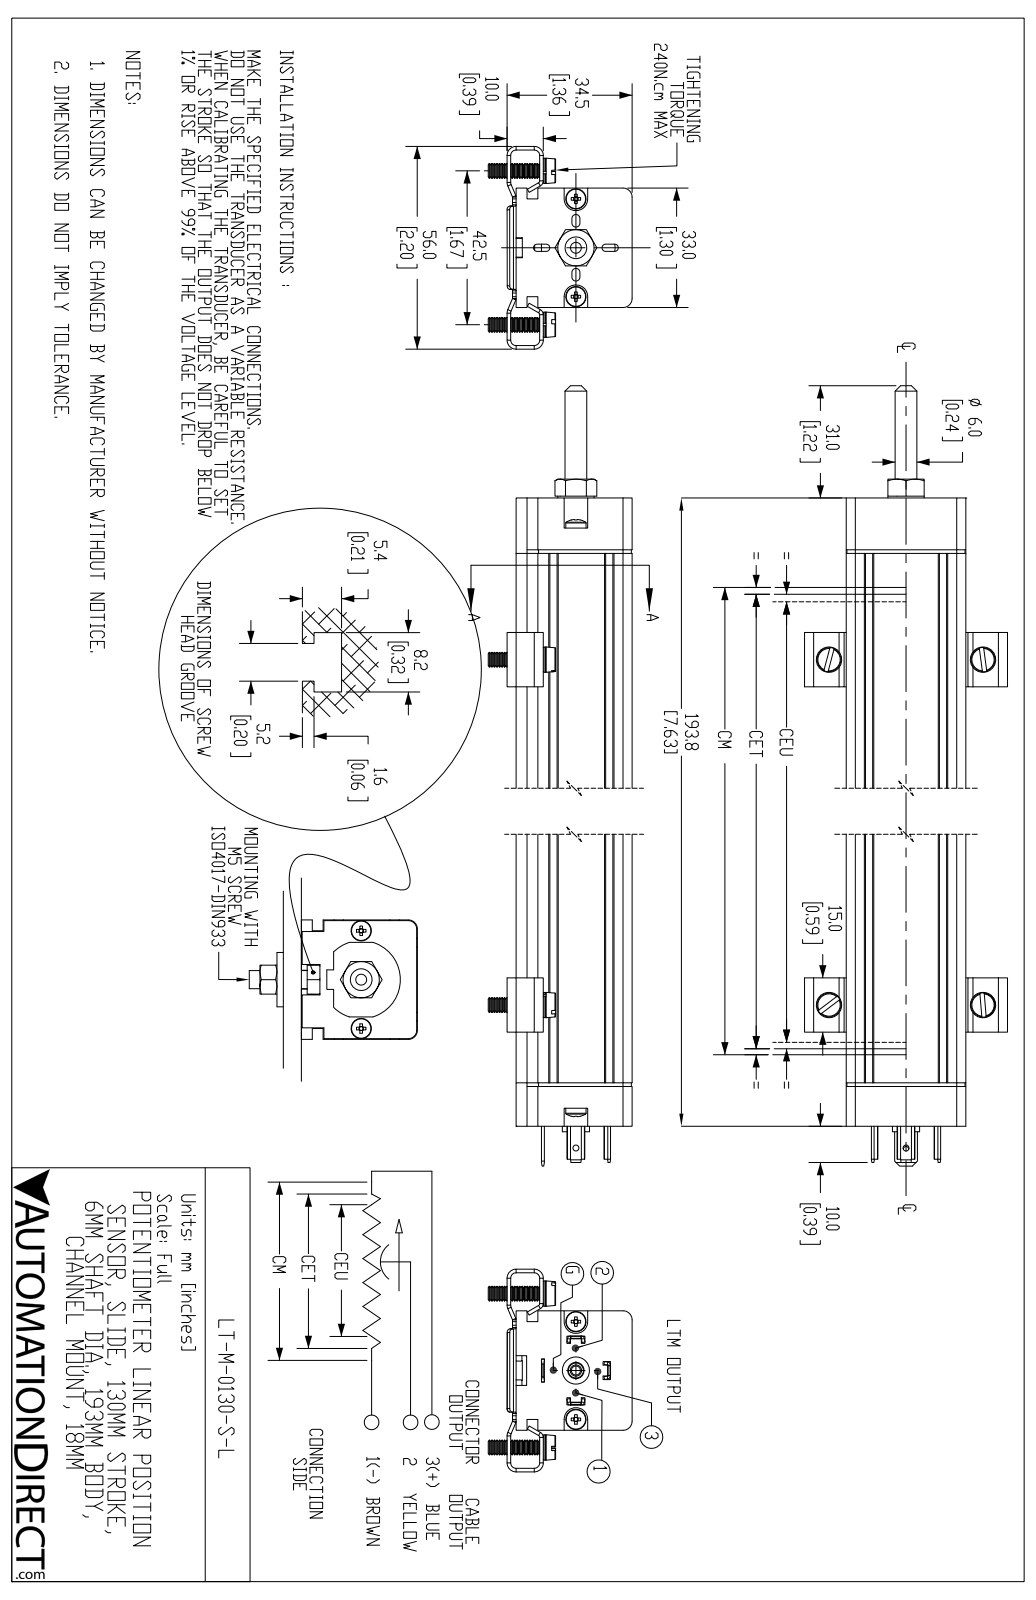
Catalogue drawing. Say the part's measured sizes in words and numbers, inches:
The part is named "LT-M-0130-S-L". Its 3-D file was written by "SolidWorks 2019 (AUTOMOTIVE_DESIGN)". It is 21 solids with 1620 faces: 696 planar, 356 cylindrical and 568 other. Overall it measures 9.977 by 2.205 by 1.563 inches. Its volume is 12.11 cubic inches and its surface area 82.45 square inches. Round holes: 4 of diameter 0.142, 2 of diameter 0.059, 2 of diameter 0.065, 2 of diameter 0.108, 2 of diameter 0.134, 2 of diameter 0.169, 1 of diameter 0.063, 1 of diameter 0.098, 1 of diameter 0.118, 1 of diameter 0.163, 1 of diameter 0.197, 1 of diameter 0.276. Round bosses or shafts: 4 of diameter 0.274, 4 of diameter 0.157, 2 of diameter 0.22, 2 of diameter 0.118, 1 of diameter 0.295, 1 of diameter 0.236, 1 of diameter 0.177, 1 of diameter 0.173. Partial cylindrical surfaces (rounded edges, fillets, slot ends): 34 of radius 0.039, 12 of radius 0.098, 10 of radius 0.059, 8 of radius 0.085, 6 of radius 0.033, 4 of radius 0.043, 2 of radius 0.024, 2 of radius 0.063. The main face-to-face distances are 1.299, 1.26, 0.118, 0.039, 1.287, 0.059, 0.213, 1.024, 0.488, 0.236. The hole center spacings are 0.484, 0.531, 1.359, 1.663, 1.673, 1.766, 1.78, 4.992.
